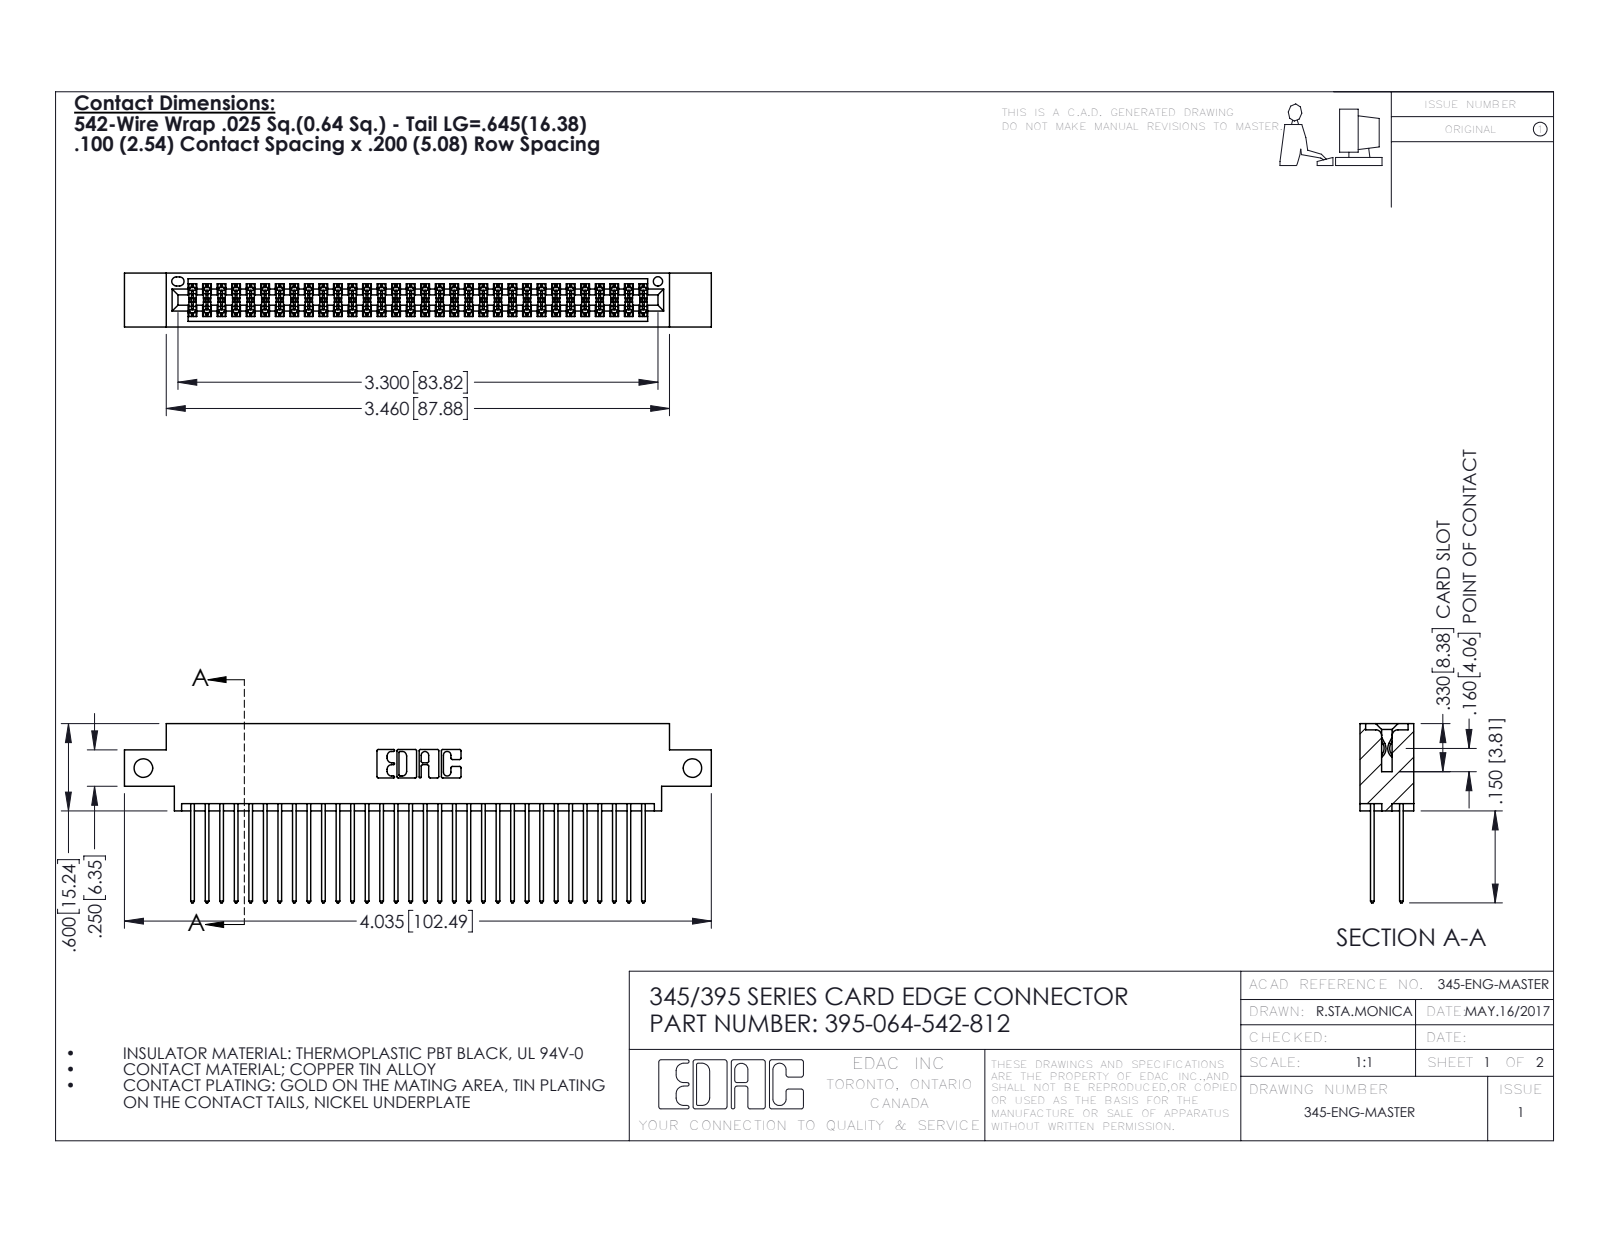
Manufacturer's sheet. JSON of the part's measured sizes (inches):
{"part_name": "345 Part_0.170 Offset - Side Mount; 345-292-001_345-293-142; 395-064-542-812", "step_written_by": "SolidWorks 2016 (CONFIG_CONTROL_DESIGN)", "units": "inches", "bodies": {"solids": 65, "faces": 3330, "planar": 2196, "cylindrical": 1134, "other": 0}, "overall_size": [4.035, 1.232, 0.37], "volume_in3": 0.608, "surface_area_in2": 24.69, "round_holes": [[0.128, 2], [0.064, 1]], "partial_cylinders_radius": [[0.006, 96], [0.01, 64], [0.01, 22], [0.007, 6], [0.031, 6], [0.026, 3], [0.014, 2], [0.019, 2]], "face_to_face_distances": [0.298, 0.072, 0.2, 0.098, 0.272, 0.025, 0.37, 0.225, 0.175, 0.149], "hole_center_spacings": [3.775]}
